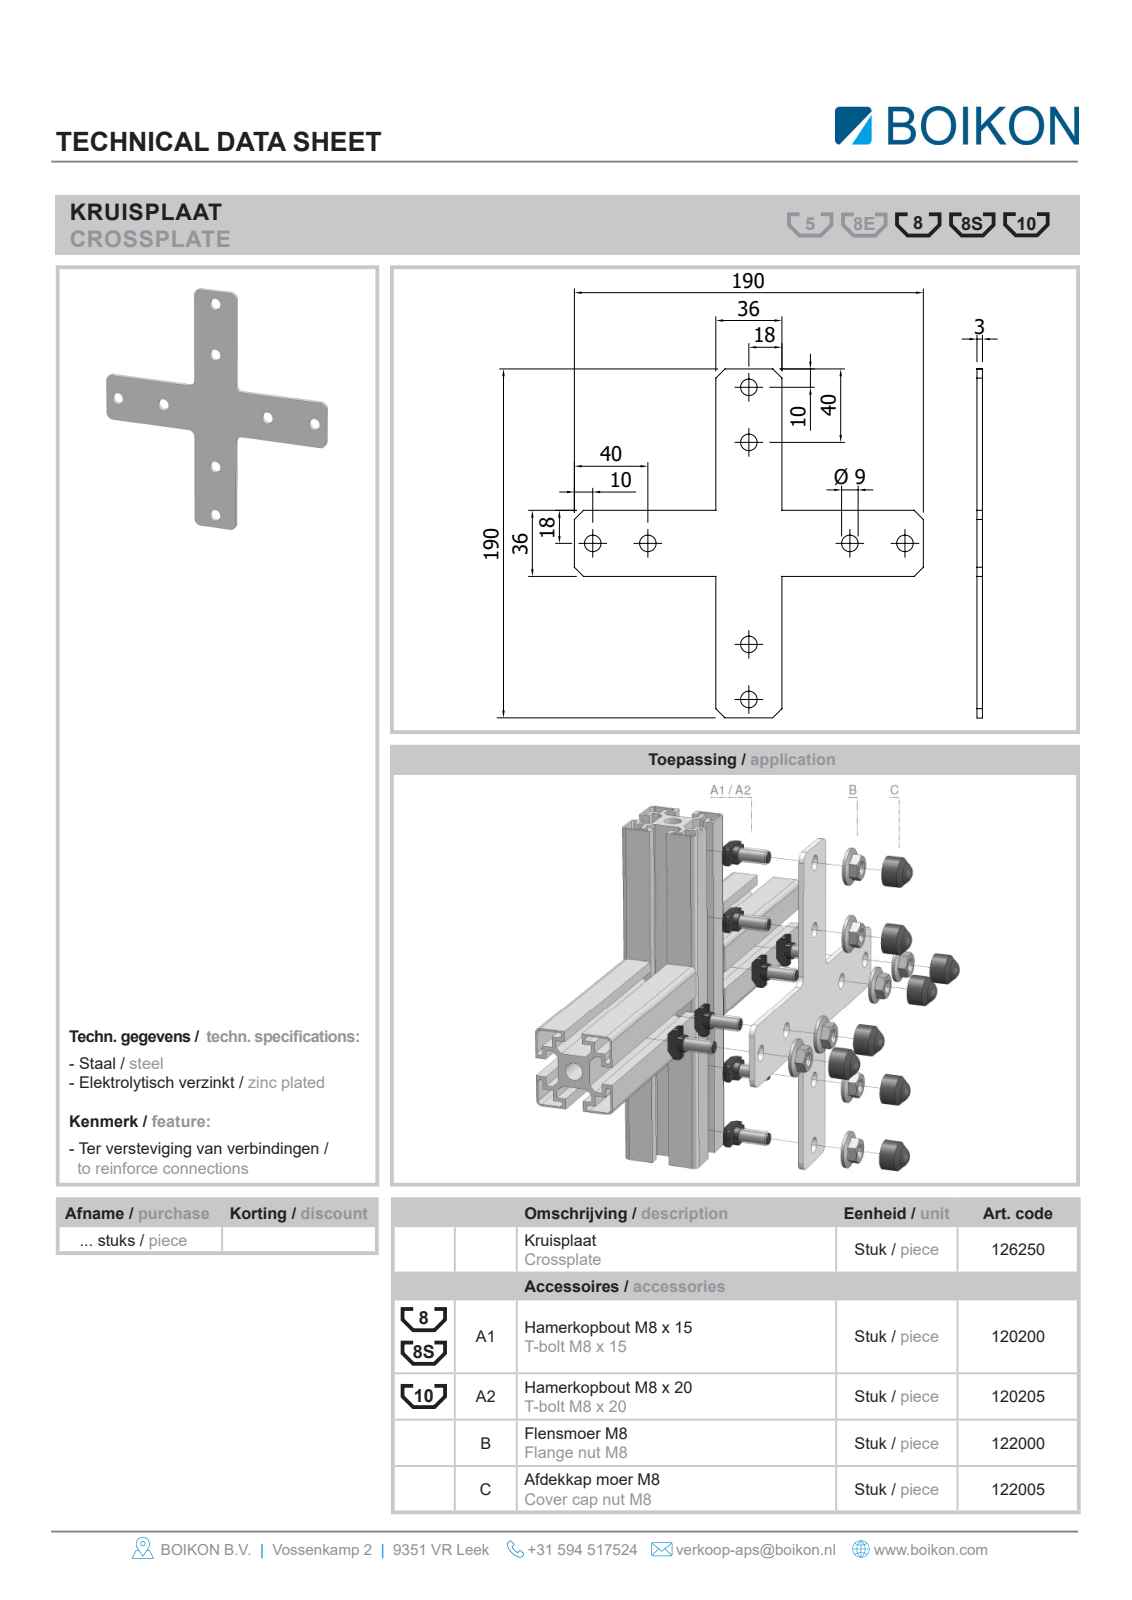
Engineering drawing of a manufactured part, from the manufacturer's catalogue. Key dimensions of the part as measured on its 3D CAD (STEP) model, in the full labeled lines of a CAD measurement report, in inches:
Part name (STEP PRODUCT): Root; 126250 KruisplaatBOIKON; 122000Flensmoer M8BOIKON; 122005Afdekkap voor moer M8BOIKON (+1 more)
STEP written by: HiCAD 2013 1802.4 Build 509 (AUTOMOTIVE_DESIGN)
Units: inches
Bodies: 25 solids, 738 faces (502 planar, 132 cylindrical, 104 other)
Overall size (bounding box): 7.52 × 7.52 × 1.213
Volume: 4.552 in³ · Surface area: 83.75 in²
Round holes (diameter × count): ⌀0.315 ×8, ⌀0.354 ×8
Round bosses / shafts (diameter × count): ⌀0.827 ×8, ⌀0.661 ×8, ⌀0.255 ×8
Partial cylindrical surfaces — rounded edges, fillets, slot ends (radius × count): R0.039 ×40, R0.197 ×28, R0.046 ×8, R0.374 ×8
Main face-to-face distances: 0.118, 0.512, 0.276, 0.453, 0.217, 0.394, 0.177, 4.432, 1.364, 0.965
Hole centre spacings: 3.787, 1.575, 2.506, 4.733, 5.118, 3.543, 6.693
